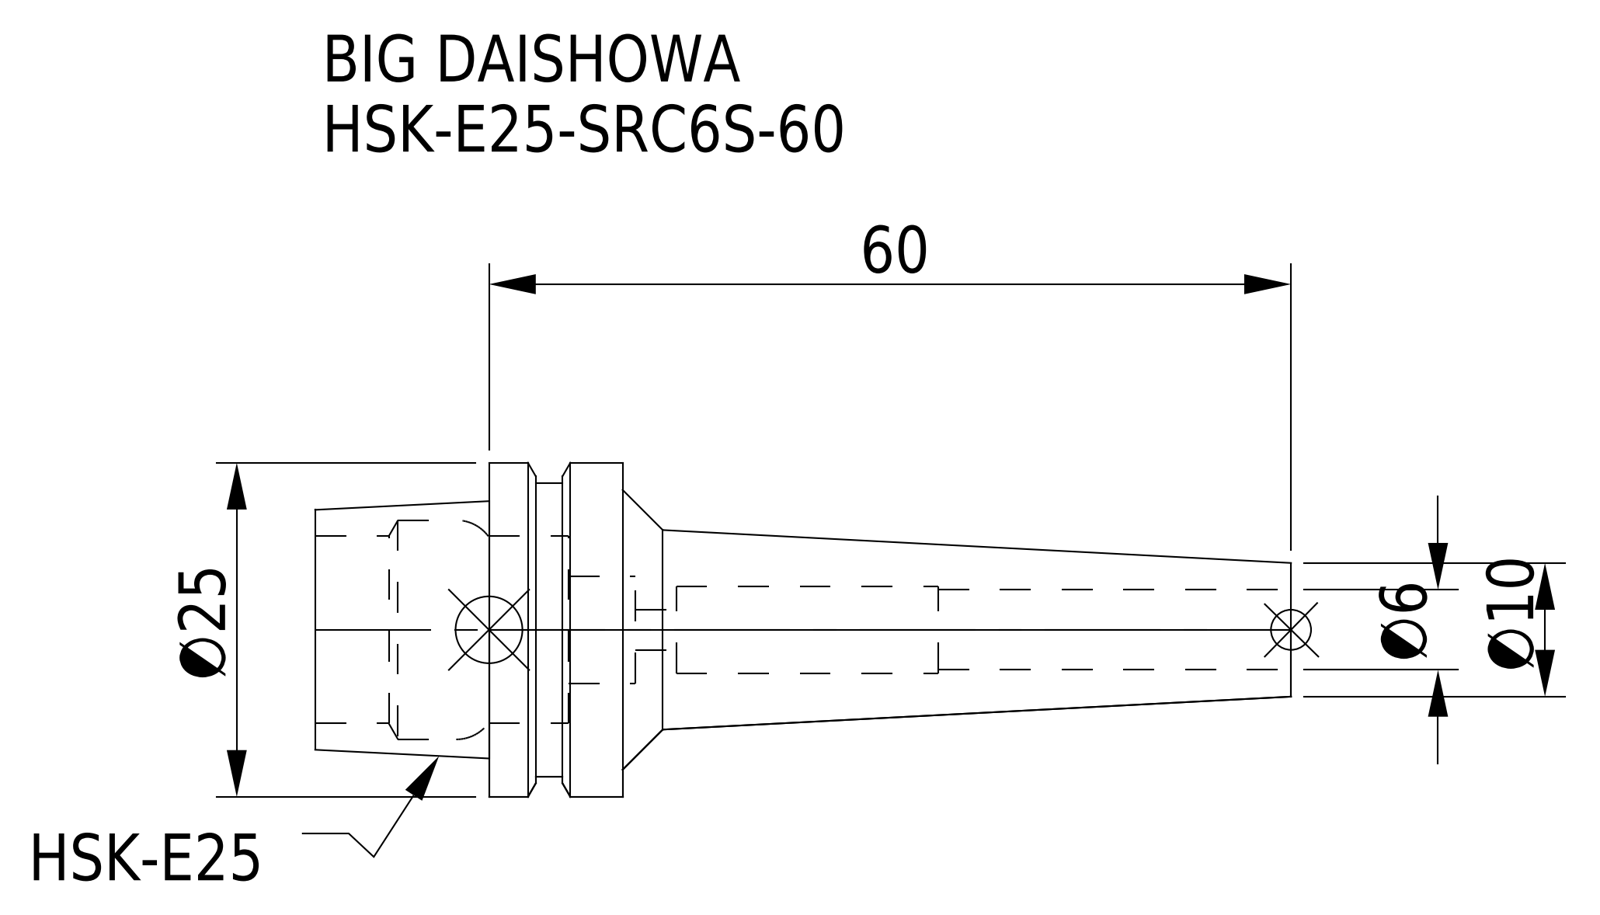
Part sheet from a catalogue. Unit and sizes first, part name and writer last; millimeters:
Units: millimetres
Overall size (bounding box): 73 × 25 × 25
Round holes (diameter × count): ⌀3 ×1, ⌀6 ×1, ⌀6.5 ×1, ⌀8 ×1, ⌀14 ×1, ⌀16.4 ×1
Round bosses / shafts (diameter × count): ⌀25 ×1, ⌀22 ×1
Main face-to-face distances: 10, 4.05, 5.95, 23, 18.95, 13, 50, 54.05, 60, 73
Volume: 9 798 mm³ · Surface area: 6 421 mm²
Bodies: 1 solid, 46 faces (10 planar, 22 cylindrical, 14 other)
Part name (STEP PRODUCT): HSK-E25-SRC6S-60
STEP written by: CREO PARAMETRIC BY PTC INC, 2016380 (AUTOMOTIVE_DESIGN)
